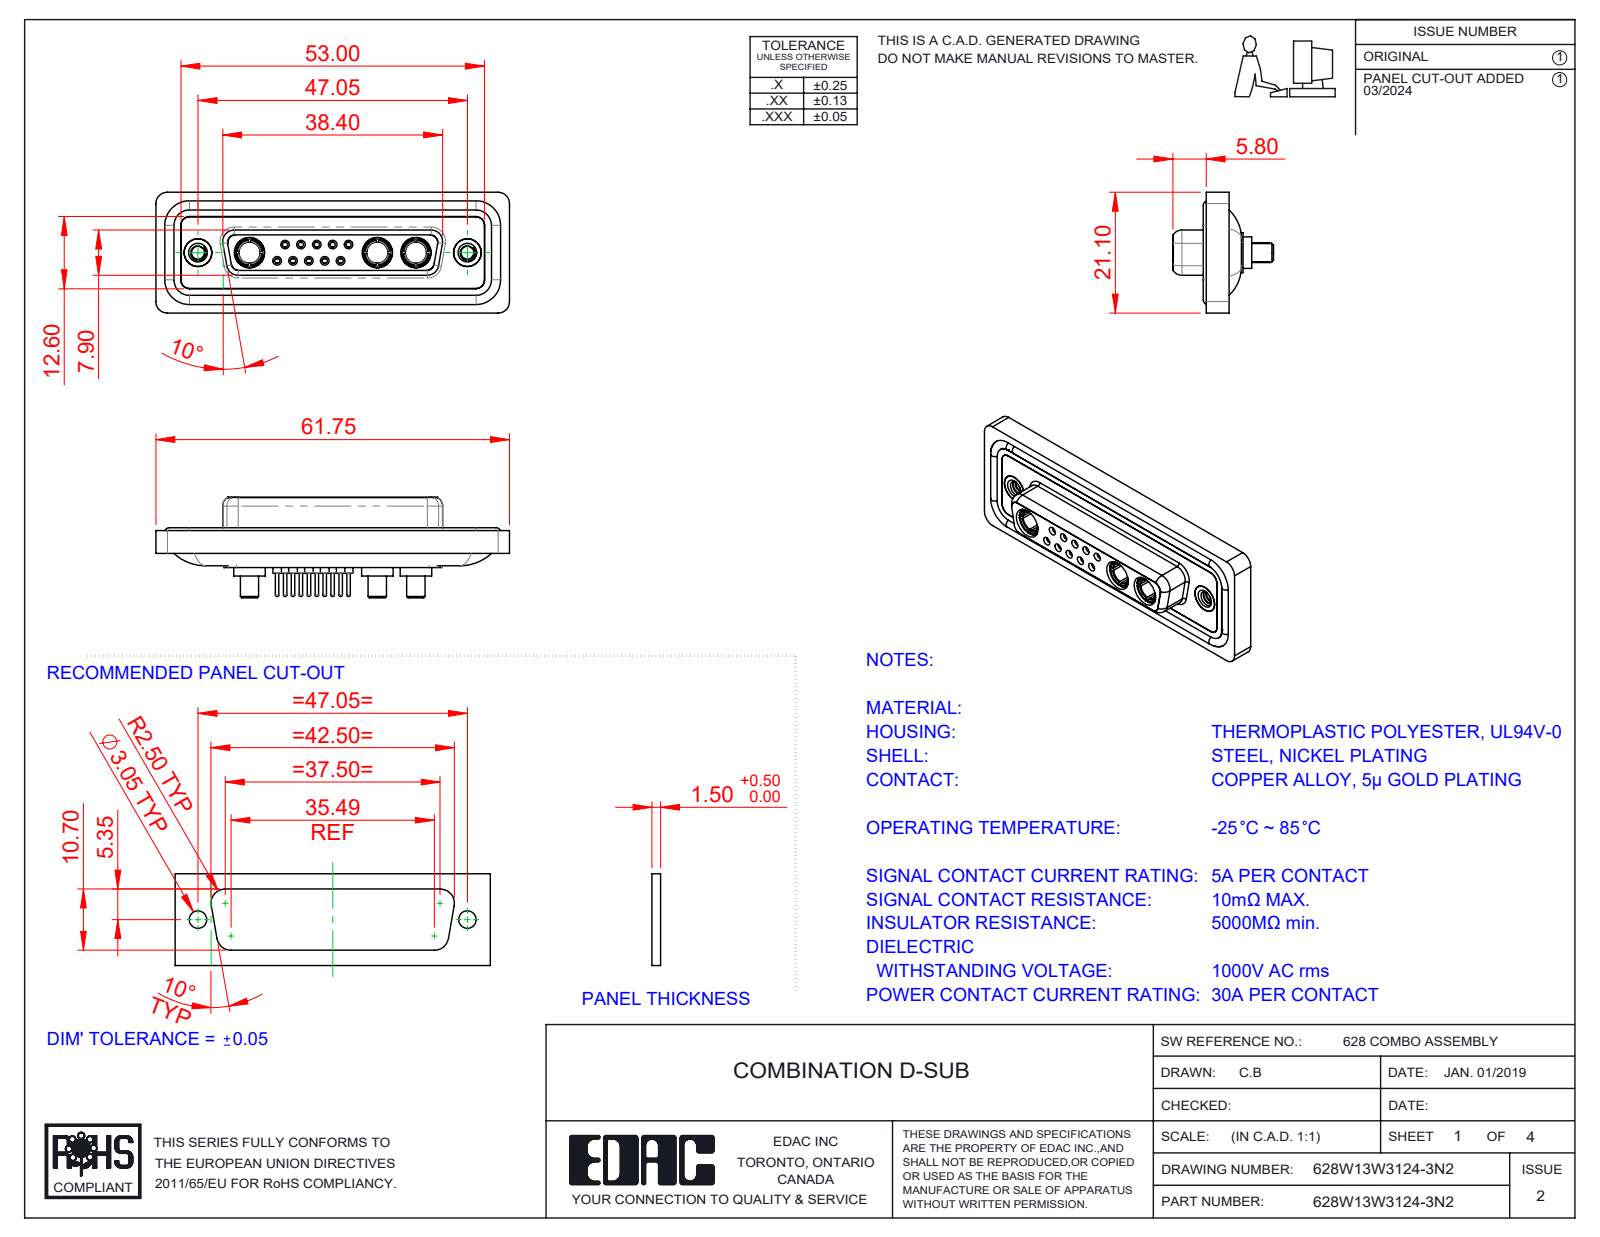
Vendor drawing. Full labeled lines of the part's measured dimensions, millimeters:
Part name (STEP PRODUCT): 628Combo Contact Row 2_24; 628Combo Waterproof Housing_25 Contacts; 628Combo Threaded Rivet_2; Power Socket_30A S (+5 more)
STEP written by: SolidWorks 2023 (CONFIG_CONTROL_DESIGN)
Units: millimetres
Bodies: 23 solids, 1158 faces (342 planar, 447 cylindrical, 369 other)
Overall size (bounding box): 61.75 × 21.1 × 17.55
Volume: 8 295 mm³ · Surface area: 13 722 mm²
Round holes (diameter × count): ⌀0.9 ×10, ⌀1.1 ×10, ⌀1.5 ×10, ⌀2 ×10, ⌀1.6 ×5, ⌀1.7 ×5, ⌀4.85 ×5, ⌀3.7 ×3, ⌀5.3 ×3, ⌀2.26 ×2, ⌀4 ×2, ⌀4.05 ×2
Round bosses / shafts (diameter × count): ⌀2.2 ×10, ⌀0.6 ×10, ⌀1.6 ×9, ⌀5.5 ×3, ⌀5.2 ×3, ⌀4.96 ×3, ⌀4.75 ×3, ⌀3.75 ×3
Partial cylindrical surfaces — rounded edges, fillets, slot ends (radius × count): R1.5 ×22, R2 ×18, R1.35 ×8, R1.6 ×8, R0.25 ×4, R0.5 ×4, R0.6 ×4, R0.65 ×4
Main face-to-face distances: 0.4, 1.8, 7.45, 5.65, 0.5, 6.6, 7.05, 1.6, 2.9, 1.1
Hole centre spacings: 3.16, 2.77, 5.03, 5.04, 5.54, 8.31, 7.49, 2.76
